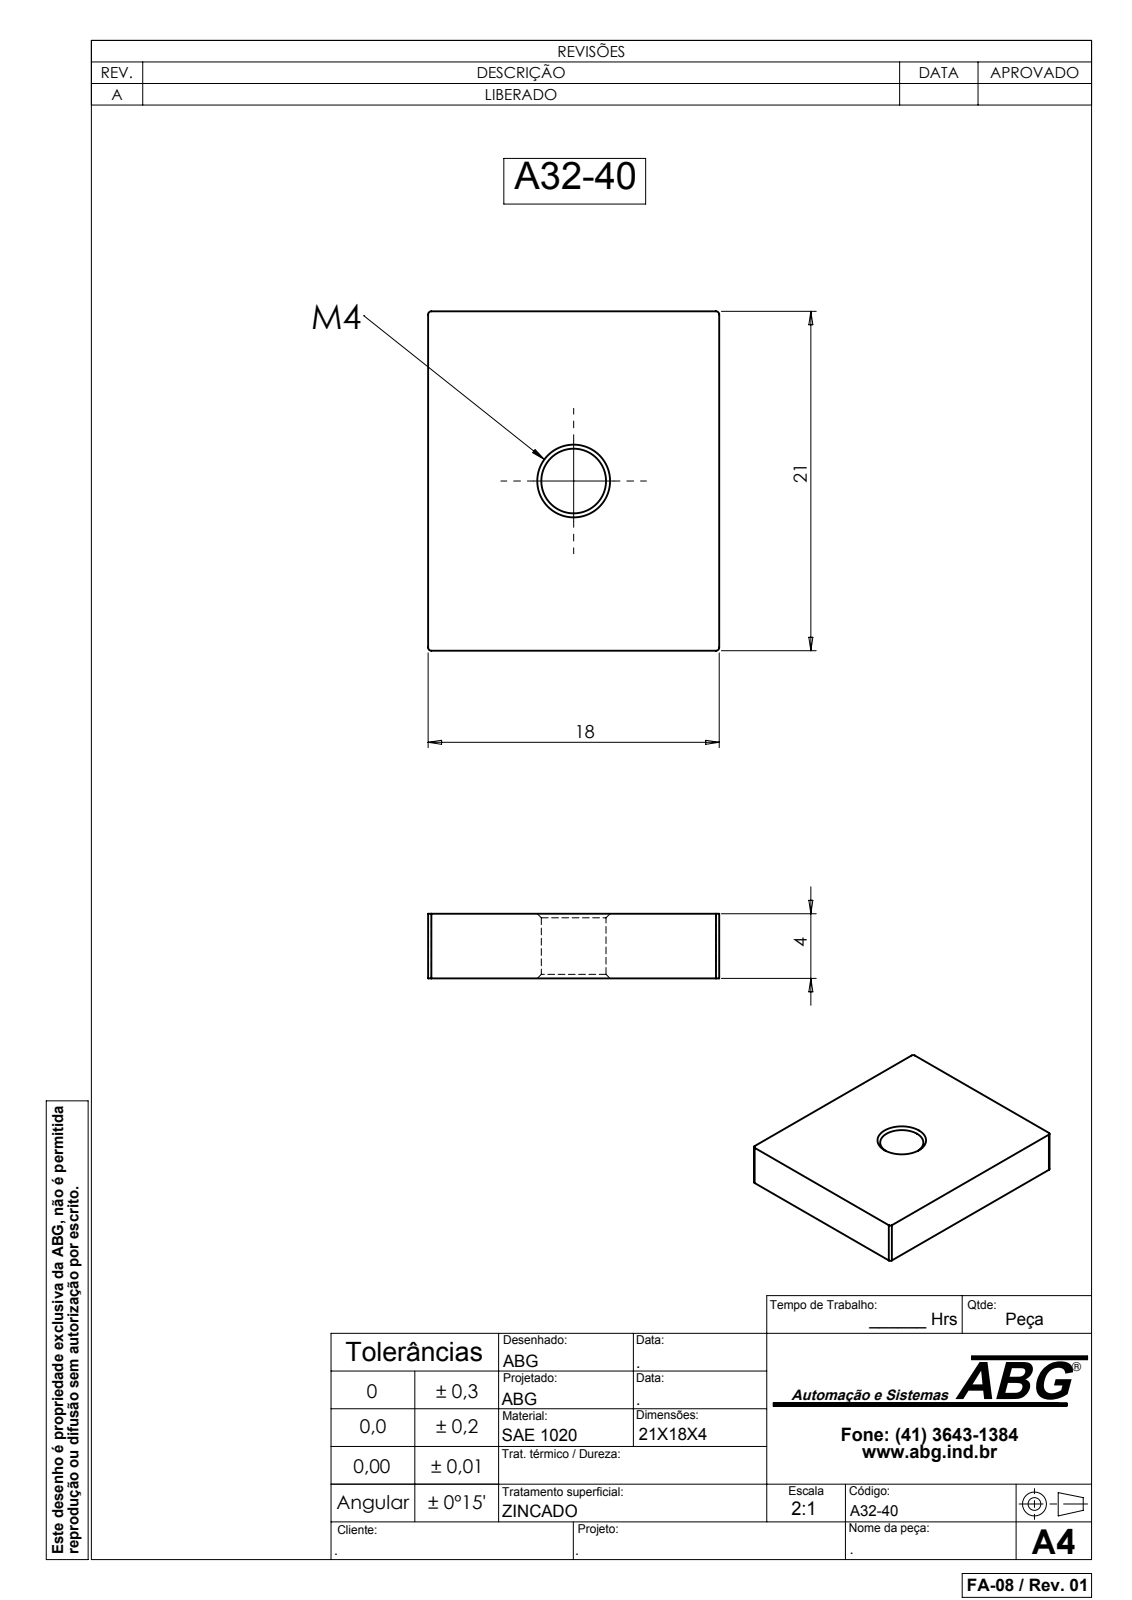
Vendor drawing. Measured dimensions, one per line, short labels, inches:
name: A32-40
written by: SolidWorks 2007 (CONFIG_CONTROL_DESIGN)
unit: in
bodies: 1 solid, 16 faces (6 planar, 6 cylindrical, 4 other)
size: 0.827 × 0.709 × 0.157
volume: 0.089 in³; area: 1.686 in²
holes: 1× ⌀0.157
rounds: 4× R0.008
face distances: 0.157, 0.709, 0.827
